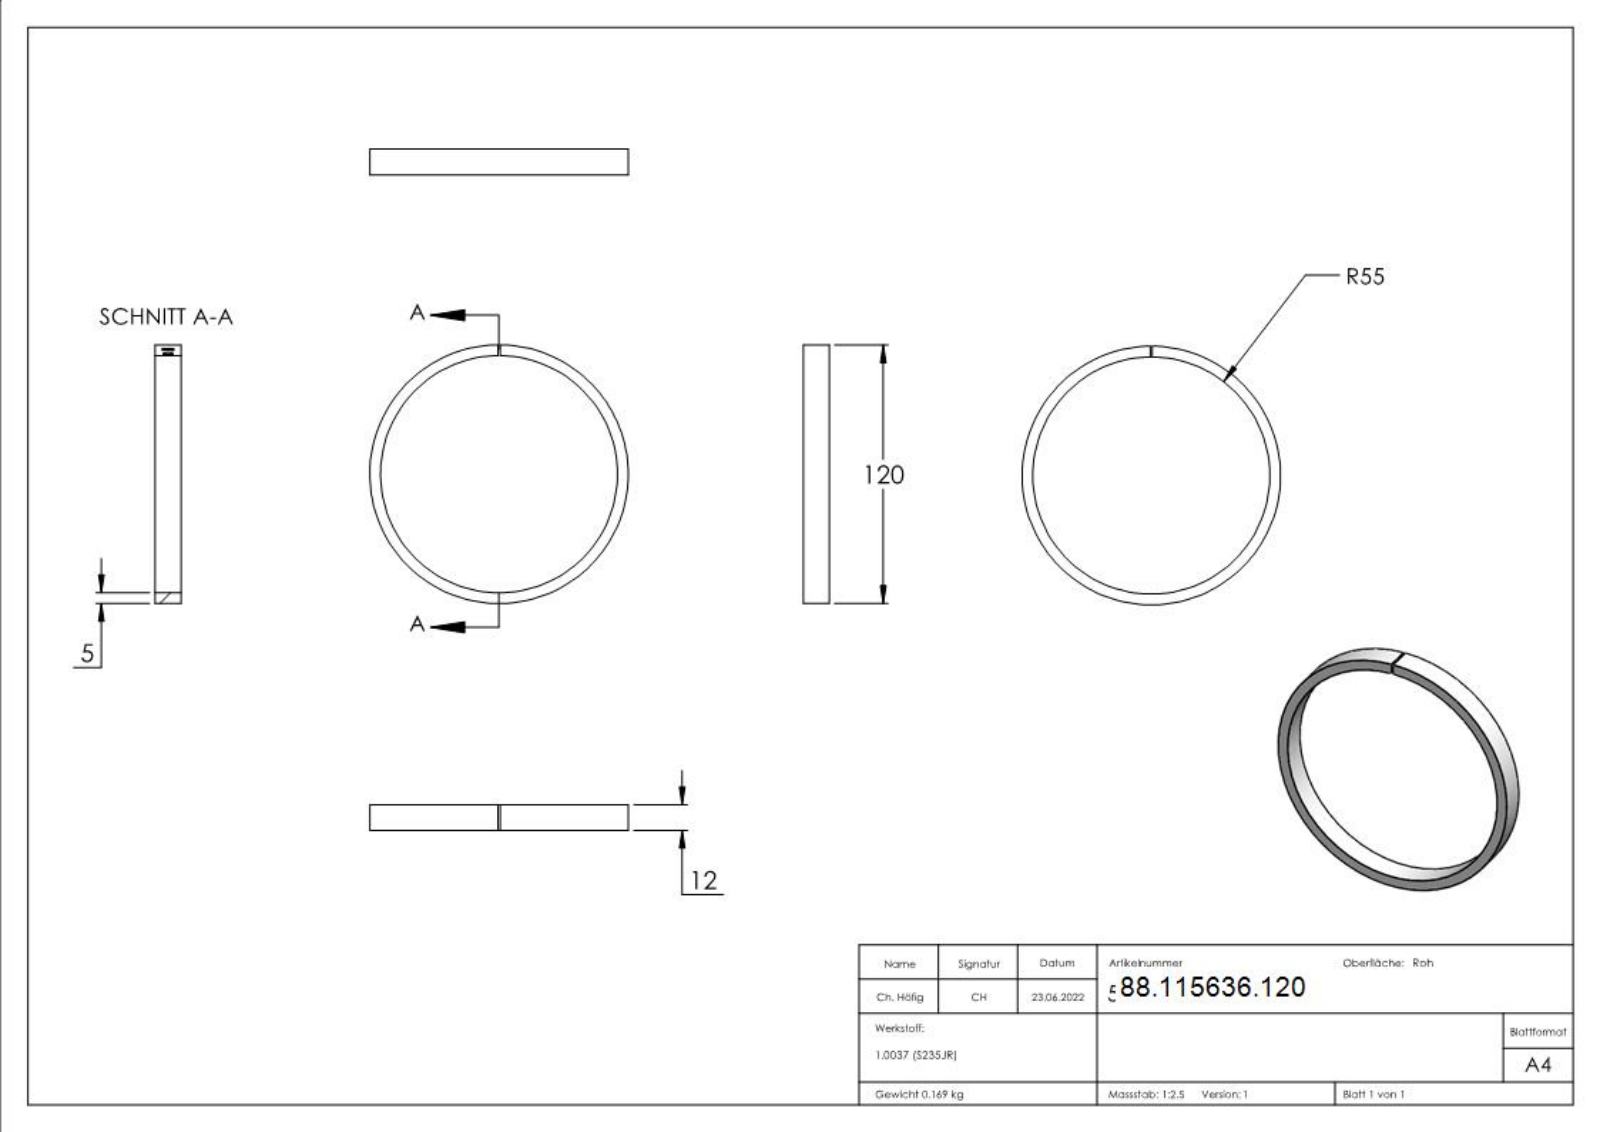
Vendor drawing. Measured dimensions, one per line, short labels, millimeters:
name: 5636-120
written by: SolidWorks 2018 (CONFIG_CONTROL_DESIGN)
unit: mm
bodies: 1 solid, 216 faces (111 planar, 2 cylindrical, 103 other)
size: 120 × 120 × 12
volume: 21 617 mm³; area: 12 375 mm²
holes: 1× ⌀110
bosses: 1× ⌀120
face distances: 12, 1, 1.1, 1.78, 0.83, 2.12, 2.45, 0.99, 2.77, 1.21
